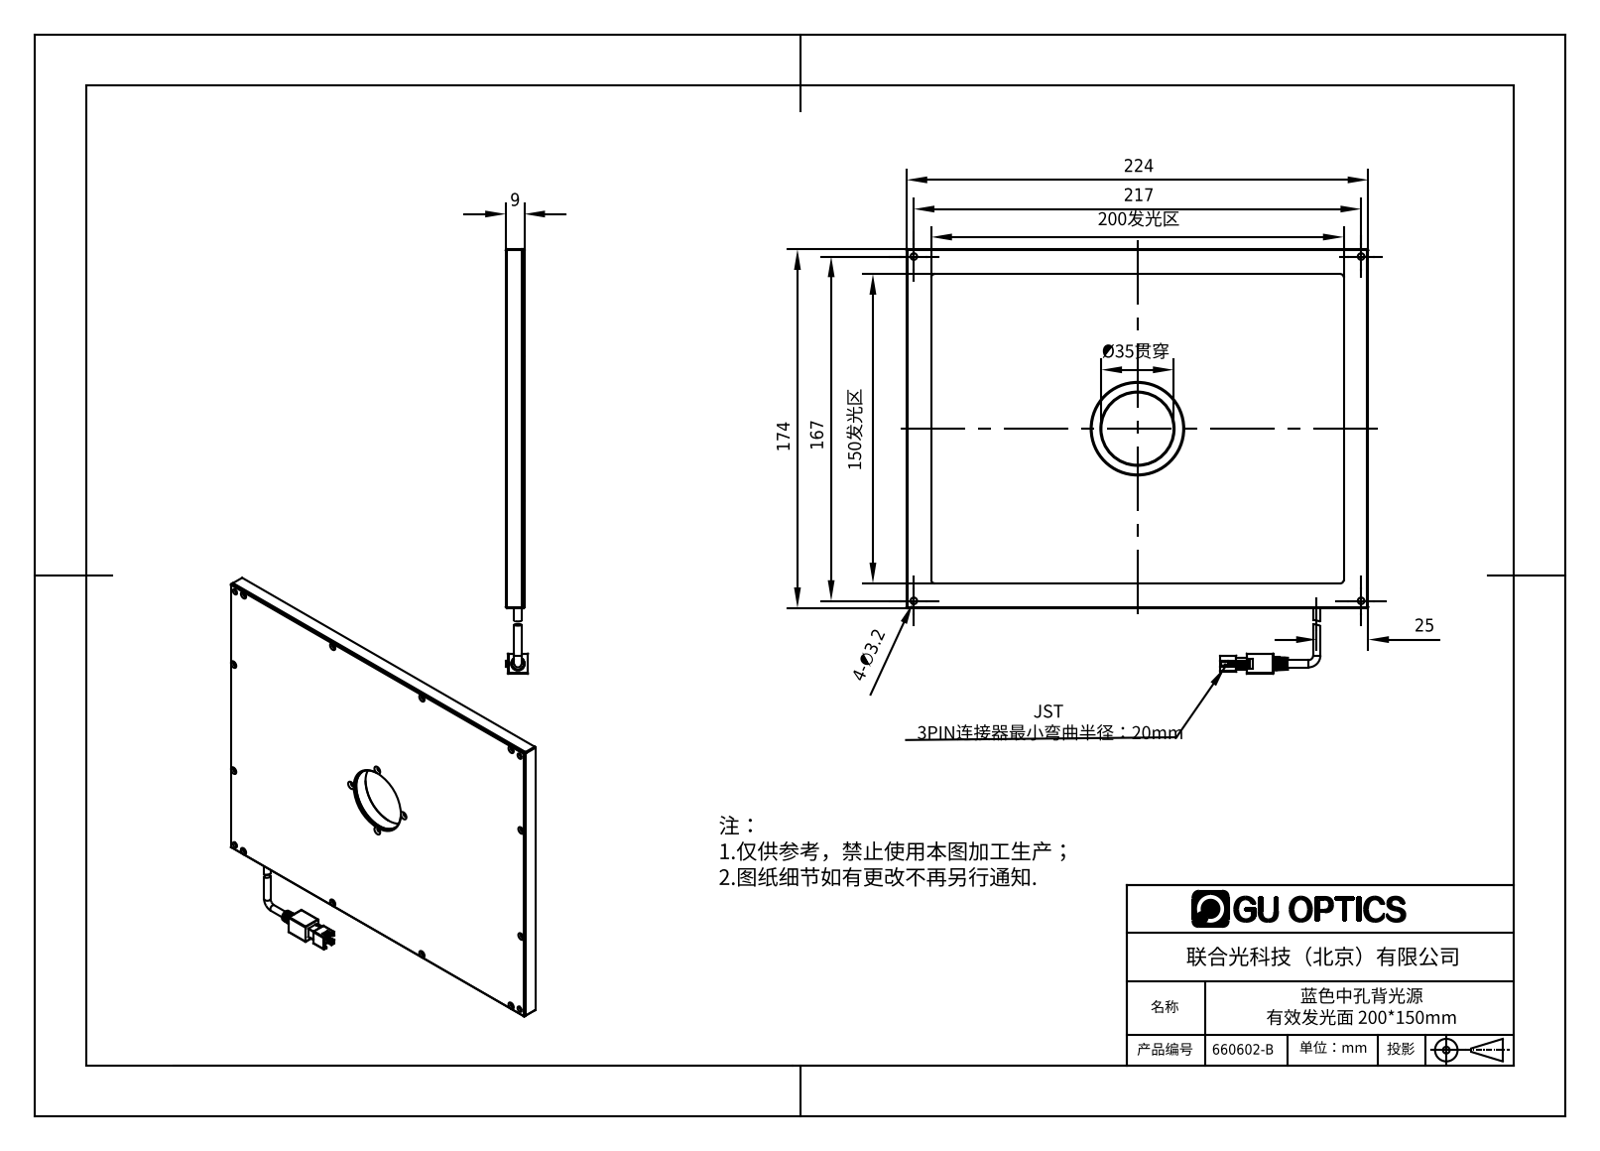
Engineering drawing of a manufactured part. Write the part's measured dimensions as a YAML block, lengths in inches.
part_name: "660602-B"
step_written_by: "SolidWorks 2016 (AUTOMOTIVE_DESIGN)"
units: inches
bodies: {solids: 10, faces: 1145, planar: 820, cylindrical: 168, other: 157}
overall_size: [8.819, 8.11, 0.427]
volume: 13.24
surface_area: 287.4
round_holes:
  - {diameter: 0.063, count: 16}
  - {diameter: 0.094, count: 12}
  - {diameter: 0.087, count: 4}
  - {diameter: 0.126, count: 4}
  - {diameter: 1.378, count: 1}
  - {diameter: 1.701, count: 1}
round_bosses_or_shafts:
  - {diameter: 0.138, count: 2}
  - {diameter: 1.787, count: 1}
  - {diameter: 1.693, count: 1}
partial_cylinders:
  - {radius: 0.004, count: 15}
  - {radius: 0.008, count: 13}
  - {radius: 0.016, count: 12}
  - {radius: 0.059, count: 6}
  - {radius: 0.079, count: 4}
  - {radius: 0.157, count: 4}
  - {radius: 0.012, count: 1}
  - {radius: 0.027, count: 1}
face_to_face_distances: [0.157, 0.059, 0.256, 0.315, 0.098, 0.039, 0.197, 0.295, 0.354, 0.217]
hole_center_spacings: [2.677, 7.172, 0.259, 0.787, 1.113, 1.91, 1.971, 2.87]
